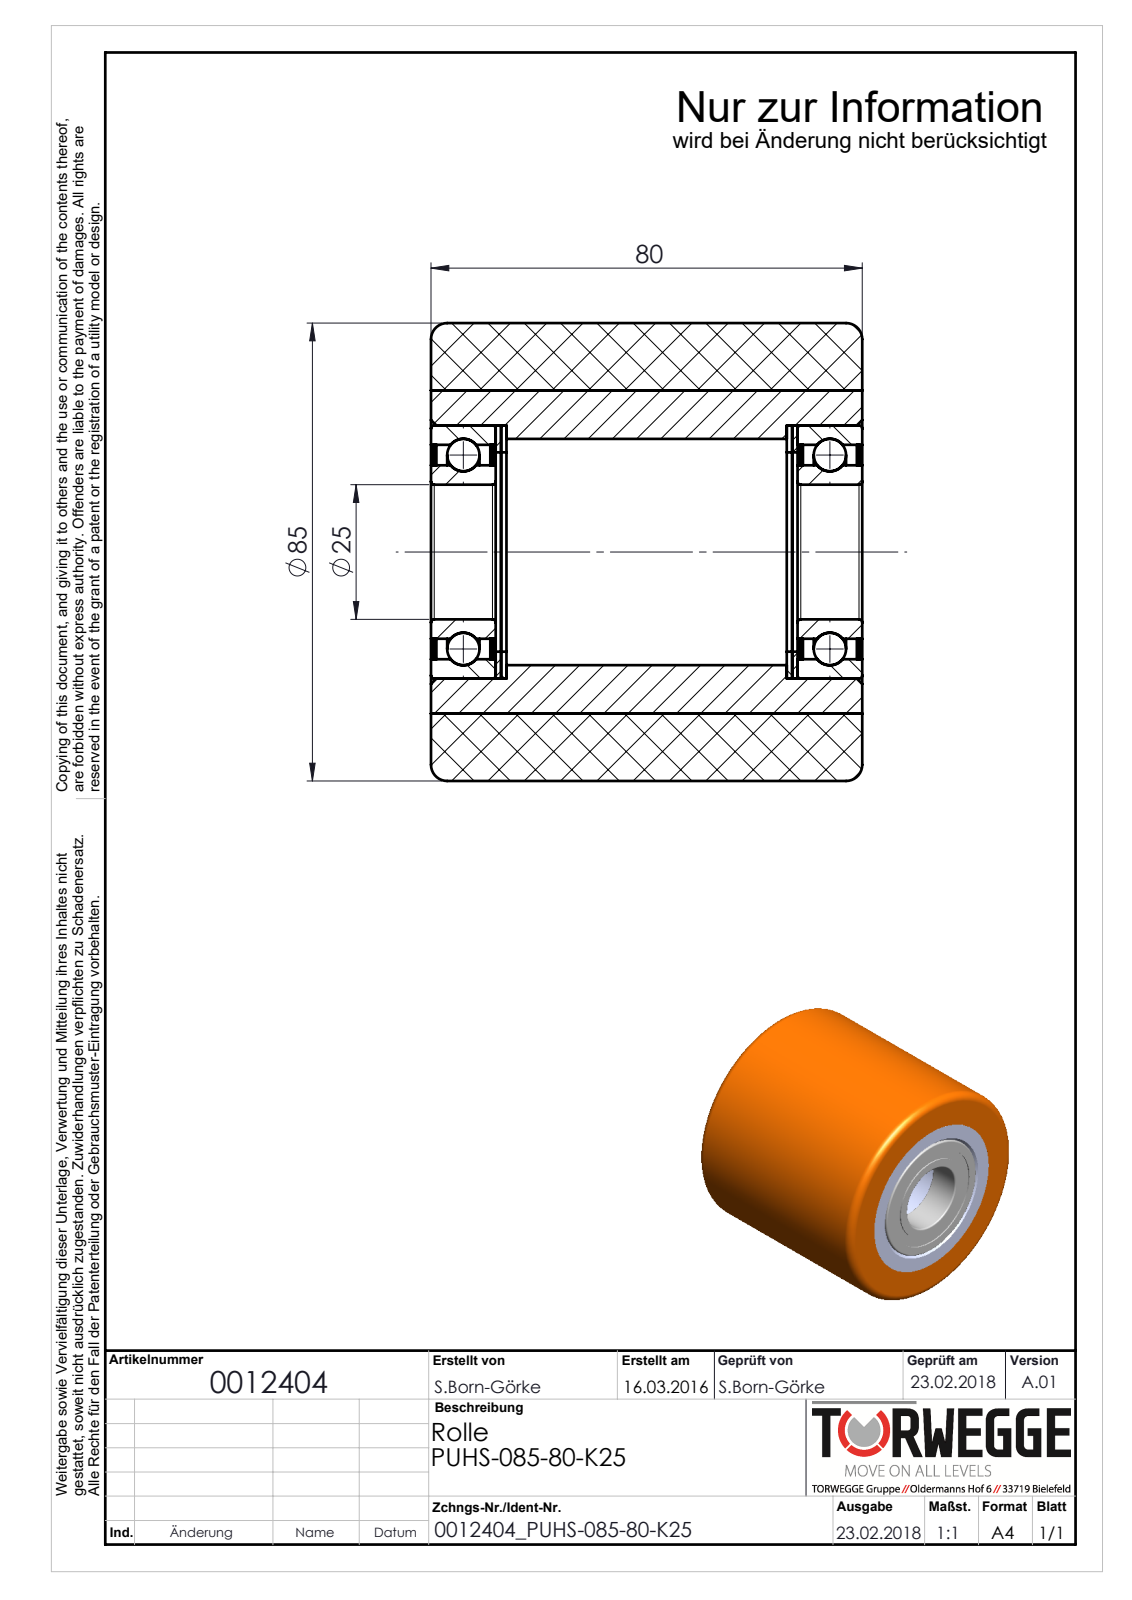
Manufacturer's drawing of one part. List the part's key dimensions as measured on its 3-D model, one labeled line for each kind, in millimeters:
Part name (STEP PRODUCT): 0012404_PUHS-085-80-K25
STEP written by: SolidWorks 2016 (AUTOMOTIVE_DESIGN)
Units: millimetres
Bodies: 16 solids, 158 faces (30 planar, 68 cylindrical, 60 other)
Overall size (bounding box): 85 × 85 × 80
Volume: 359 662 mm³ · Surface area: 98 799 mm²
Round holes (diameter × count): ⌀25 ×1, ⌀32.2 ×1, ⌀37 ×1, ⌀39.8 ×1, ⌀42 ×1, ⌀60 ×1
Round bosses / shafts (diameter × count): ⌀85 ×1, ⌀47 ×1
Main face-to-face distances: 1, 68, 80, 12, 0.5, 13, 67, 55, 54, 66
